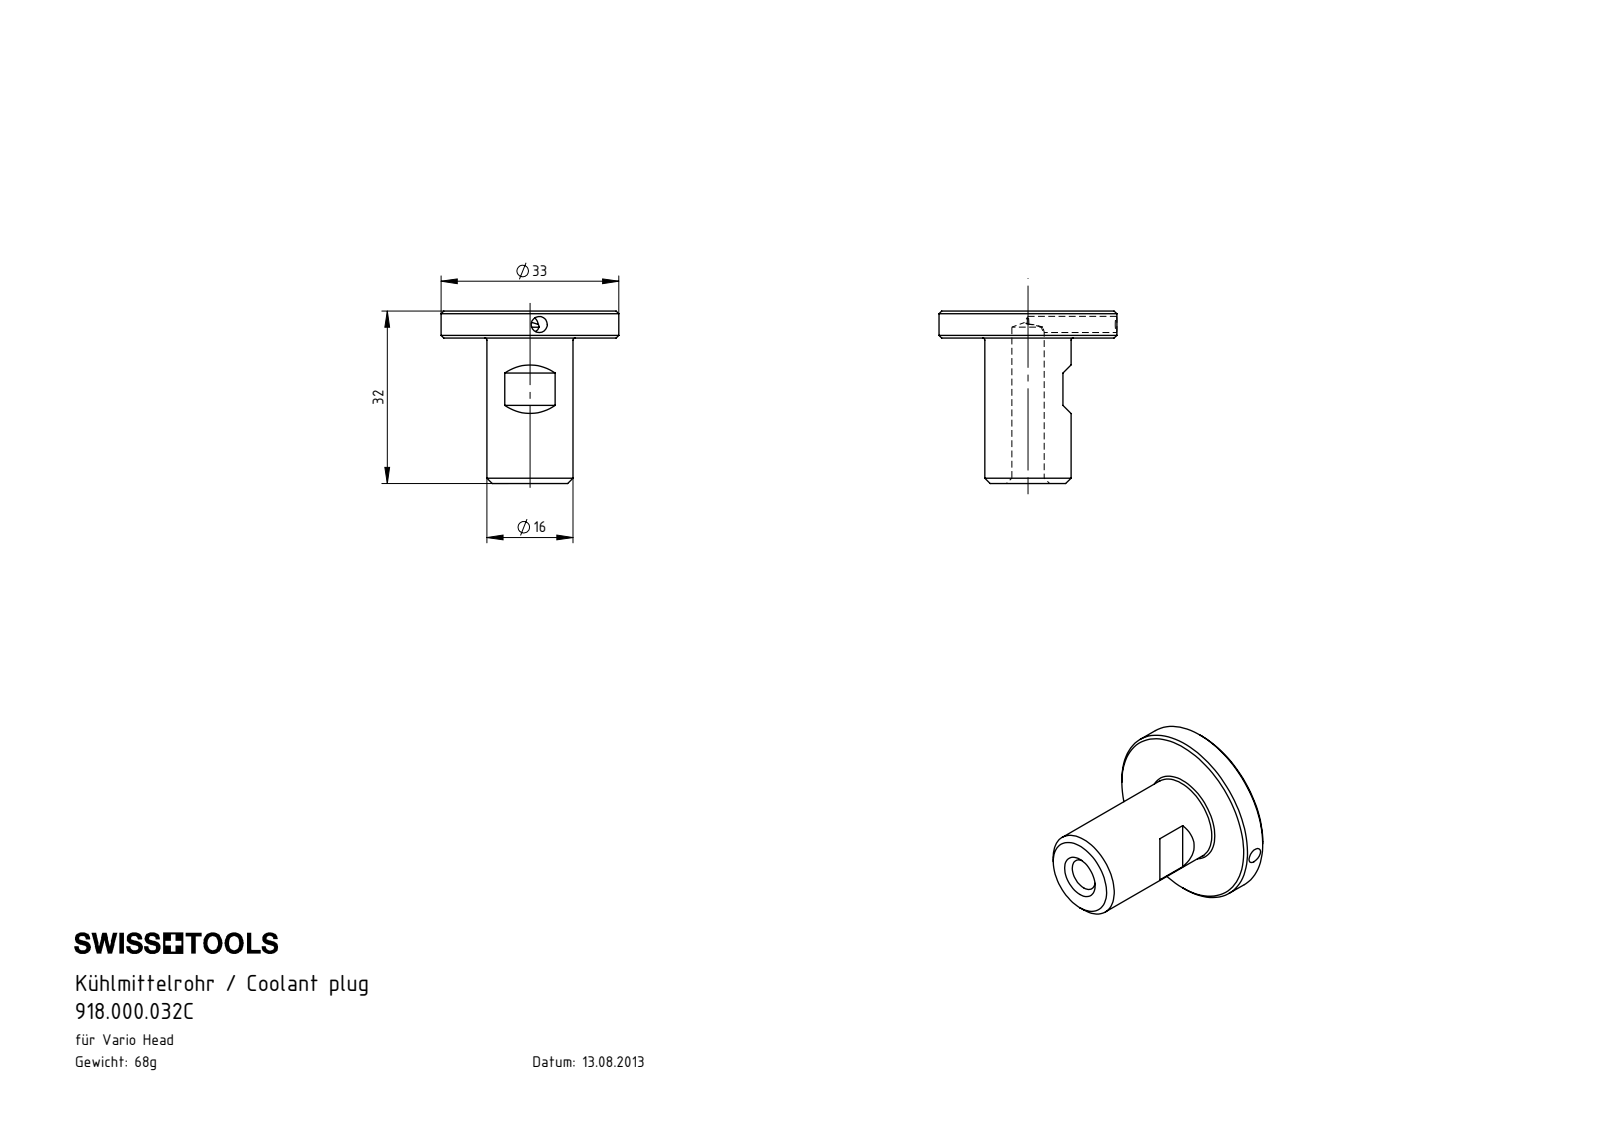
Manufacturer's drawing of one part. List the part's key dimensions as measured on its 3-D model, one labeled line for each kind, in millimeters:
Part name (STEP PRODUCT): 918.000.032C
STEP written by: SolidWorks 2022 (CONFIG_CONTROL_DESIGN)
Units: millimetres
Bodies: 1 solid, 28 faces (6 planar, 8 cylindrical, 14 other)
Overall size (bounding box): 33 × 33 × 32
Volume: 8 641 mm³ · Surface area: 4 154 mm²
Round holes (diameter × count): ⌀3 ×1, ⌀6 ×1
Round bosses / shafts (diameter × count): ⌀33 ×1, ⌀16 ×1
Main face-to-face distances: 5, 27, 32
